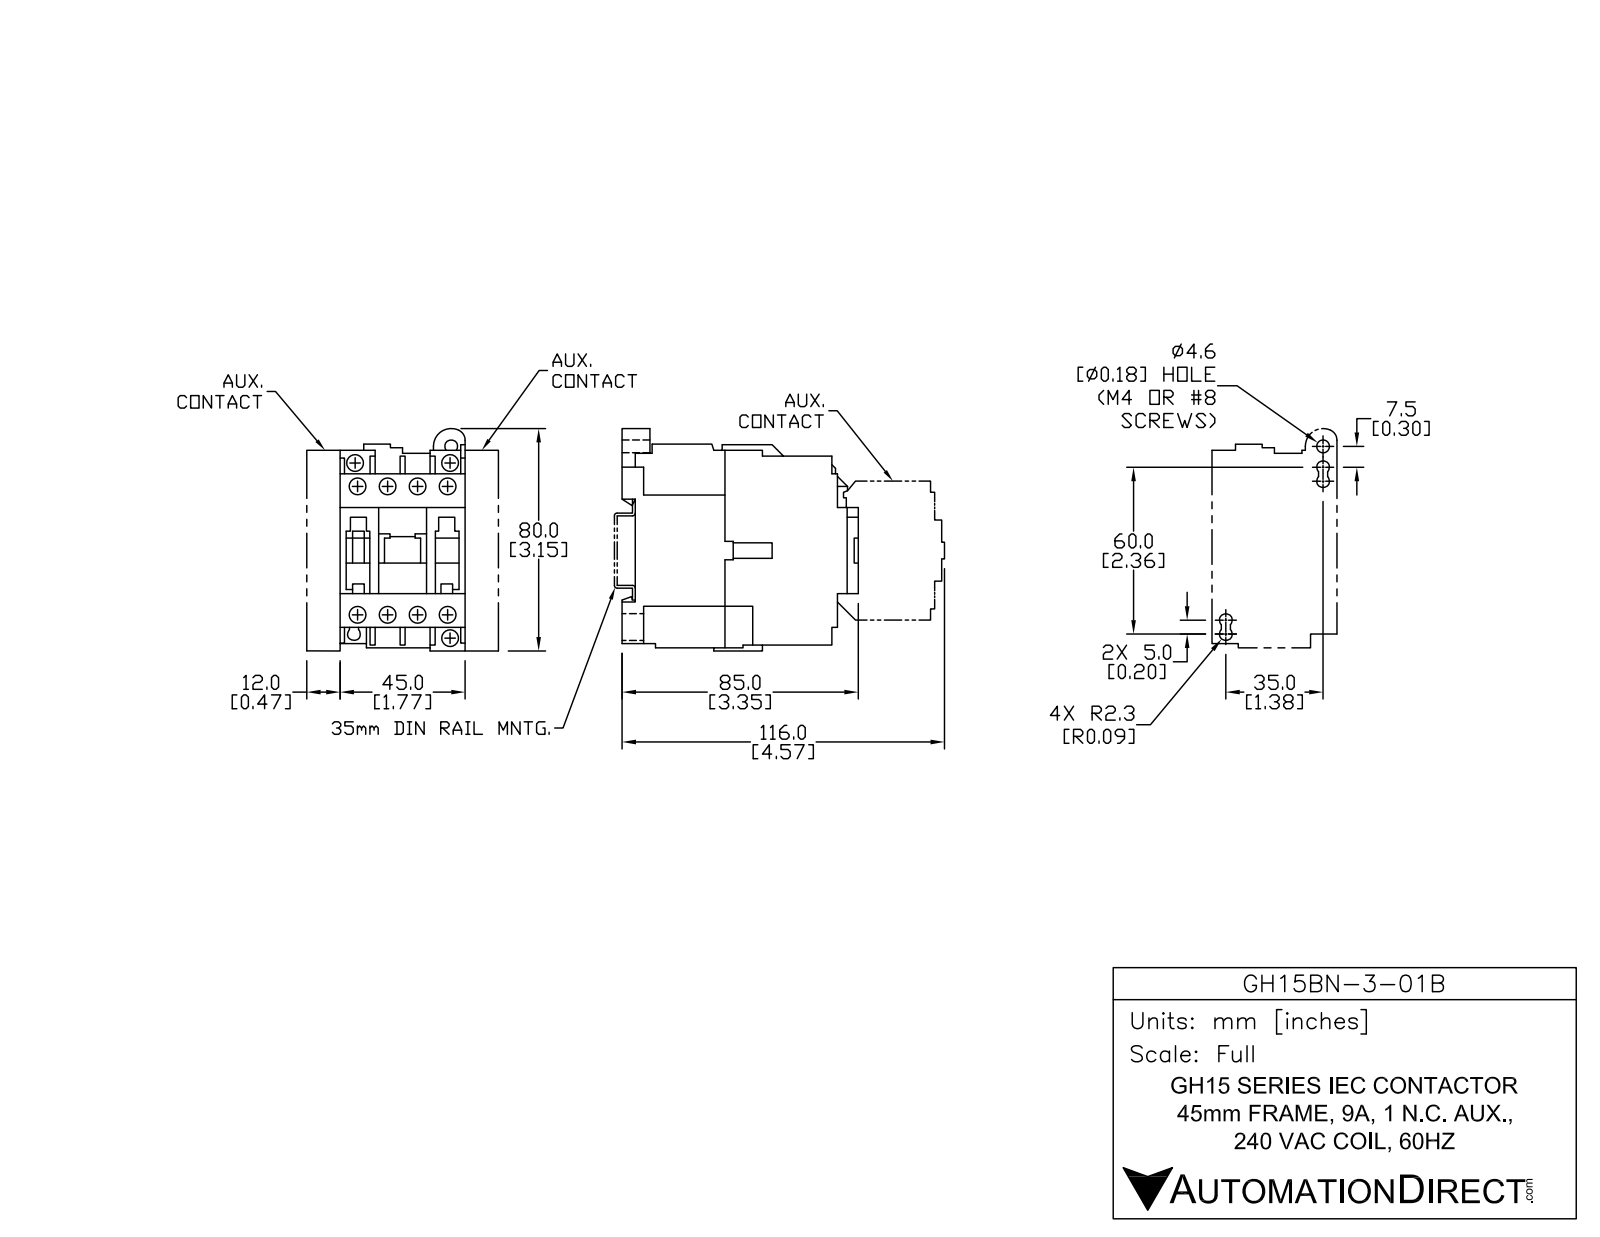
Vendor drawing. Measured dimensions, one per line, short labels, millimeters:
name: GH15BN-3-01B
written by: SolidWorks 2009 (AUTOMOTIVE_DESIGN)
unit: mm
bodies: 1 solid, 672 faces (451 planar, 65 cylindrical, 156 other)
size: 85.5 × 80 × 45
volume: 196 351 mm³; area: 35 792 mm²
holes: 9× ⌀6.25, 2× ⌀6.5, 1× ⌀4.6
rounds: 10× R1, 8× R2.3, 8× R4.75, 2× R3, 1× R4.99, 1× R5
face distances: 45, 9.5, 35.5, 12.12, 23.38, 8, 7, 33.75, 10.38, 32.87
hole spacings: 11.25, 47.12, 22.5, 45.76, 50.99, 7.62, 33.75, 53.38
